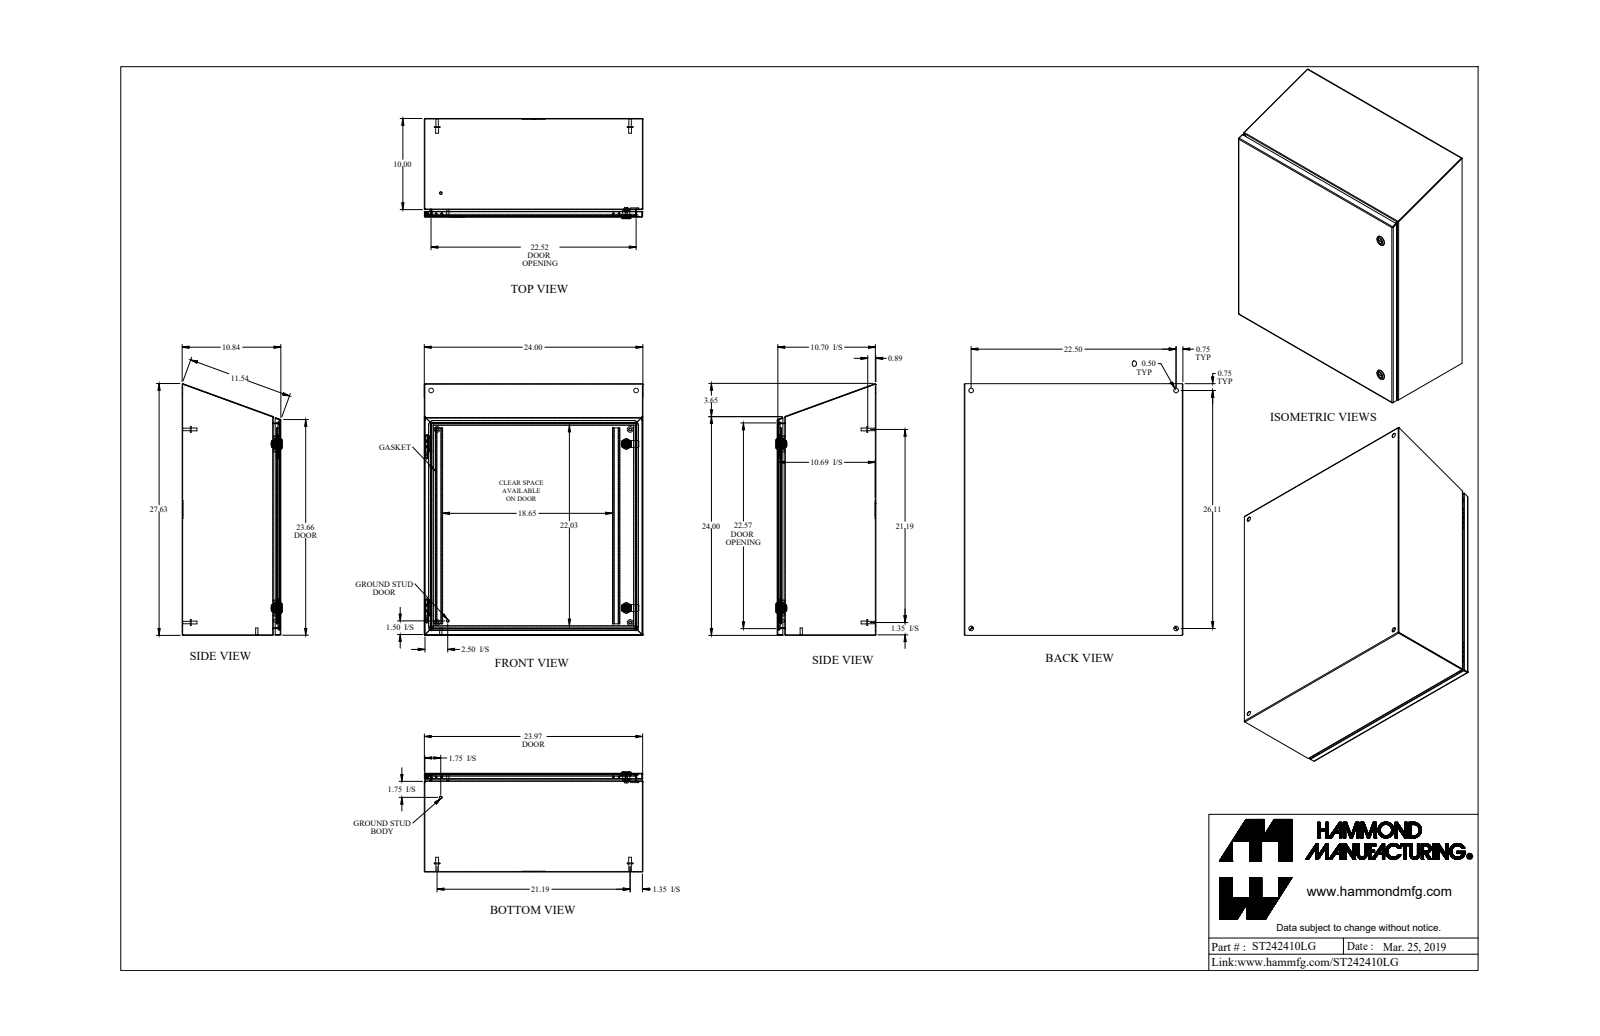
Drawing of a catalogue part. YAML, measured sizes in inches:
part_name: "ST242410LG"
step_written_by: "SolidWorks 2018 (AUTOMOTIVE_DESIGN)"
units: inches
bodies: {solids: 29, faces: 766, planar: 394, cylindrical: 248, other: 124}
overall_size: [27.614, 24, 10.997]
volume: 160.6
surface_area: 5244
round_holes:
  - {diameter: 0.5, count: 4}
  - {diameter: 0.232, count: 2}
  - {diameter: 0.625, count: 2}
  - {diameter: 0.785, count: 2}
  - {diameter: 0.172, count: 1}
  - {diameter: 0.24, count: 1}
  - {diameter: 0.242, count: 1}
round_bosses_or_shafts:
  - {diameter: 0.625, count: 4}
  - {diameter: 0.313, count: 4}
  - {diameter: 0.27, count: 4}
  - {diameter: 1.1, count: 2}
  - {diameter: 0.525, count: 2}
  - {diameter: 0.281, count: 2}
  - {diameter: 0.25, count: 2}
  - {diameter: 0.455, count: 1}
partial_cylinders:
  - {radius: 0.029, count: 15}
  - {radius: 0.086, count: 15}
  - {radius: 0.188, count: 13}
  - {radius: 0.043, count: 12}
  - {radius: 0.081, count: 12}
  - {radius: 0.006, count: 4}
  - {radius: 0.036, count: 4}
  - {radius: 0.062, count: 4}
face_to_face_distances: [0.057, 10.765, 10.708, 0.072, 10.837, 10.78, 23.943, 23.886, 24, 0.057]
hole_center_spacings: [22.5, 26.114, 34.47, 2.494, 5.961, 18, 20.279, 21.544]
